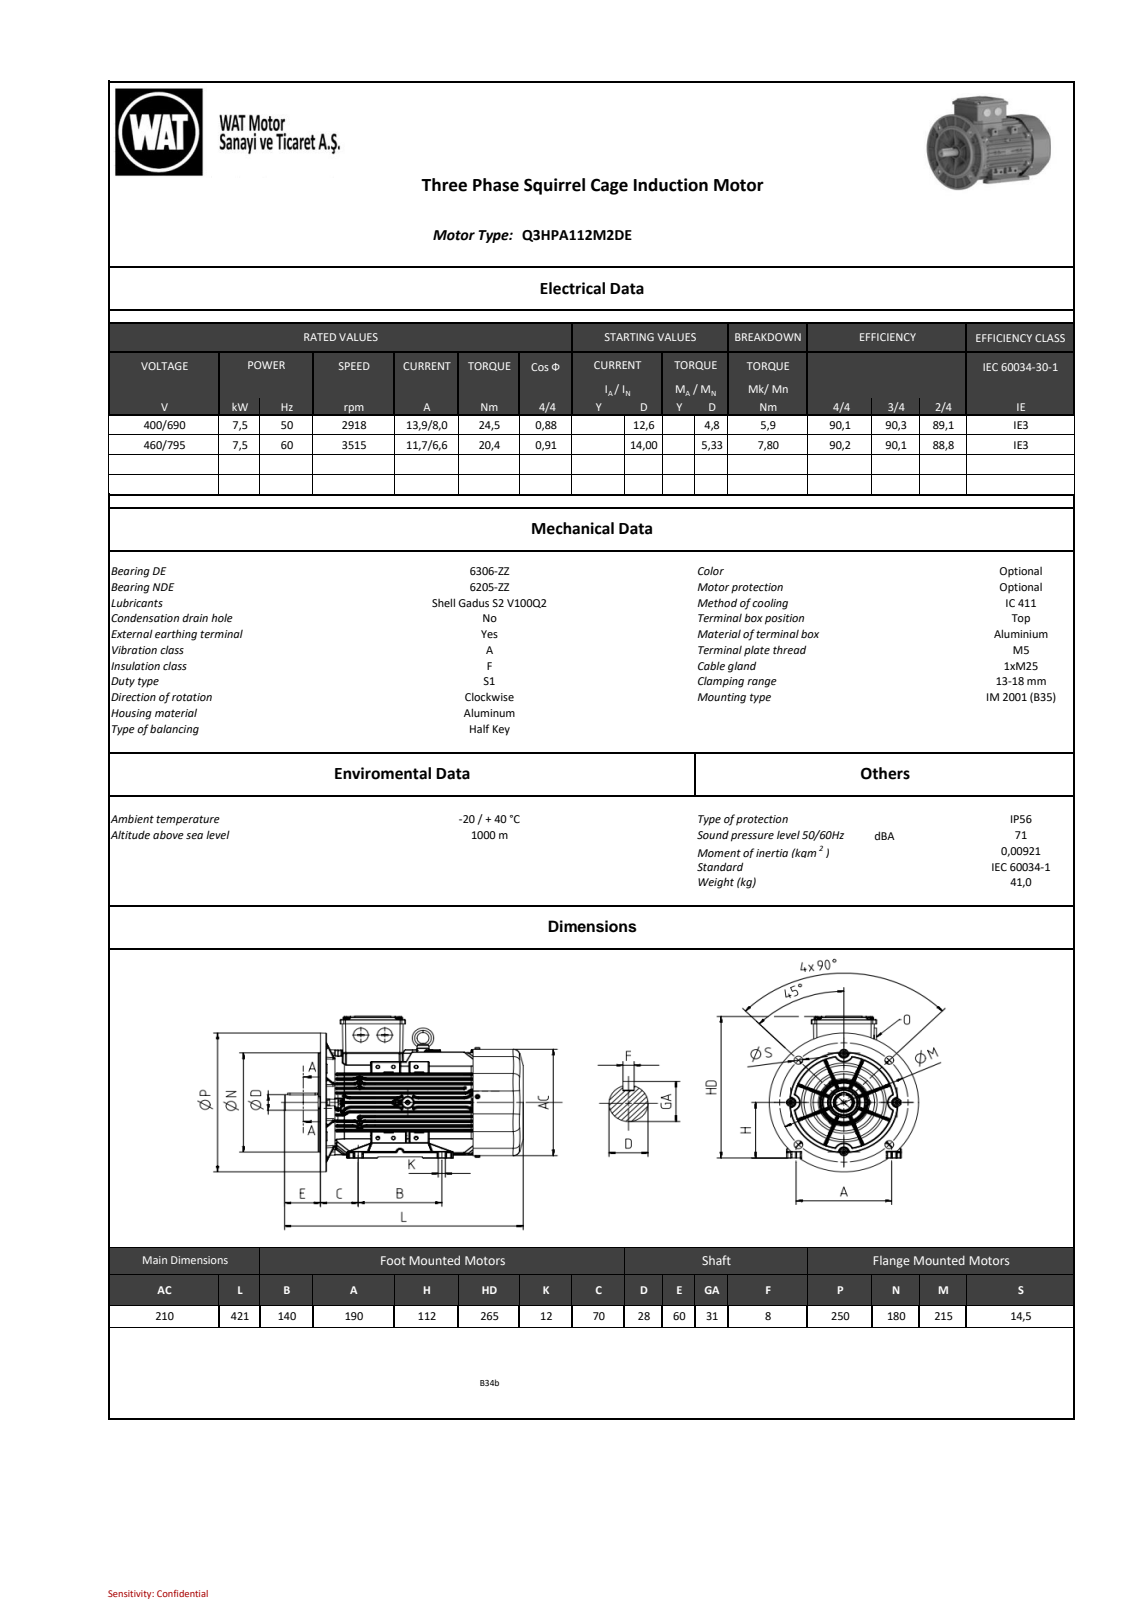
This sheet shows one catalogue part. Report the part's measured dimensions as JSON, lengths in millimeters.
{"part_name": "QH series_ 112_B35 _DEEP COVER__stp_objects", "step_written_by": "SIEMENS PLM Software NX2206.8101 (AUTOMOTIVE_DESIGN)", "units": "millimeters", "bodies": {"solids": 0, "faces": 8116, "planar": 1708, "cylindrical": 3101, "other": 3307}, "overall_size": [421, 287.37, 249.75], "round_holes": [[3.5, 2], [4.6, 2], [8, 1], [8.5, 1], [47, 1]], "round_bosses_or_shafts": [[8, 8], [13, 4], [25, 2], [188, 1], [180, 1], [35.83, 1], [30, 1], [29.5, 1]], "partial_cylinders_radius": [[2, 679], [0.8, 635], [1, 544], [0.5, 267], [3, 175], [4, 12], [6, 12], [10, 10]], "face_to_face_distances": [1, 21.5, 10.99, 35.96, 99.54, 24.97, 8.16, 112.88, 89.87, 90.43]}
